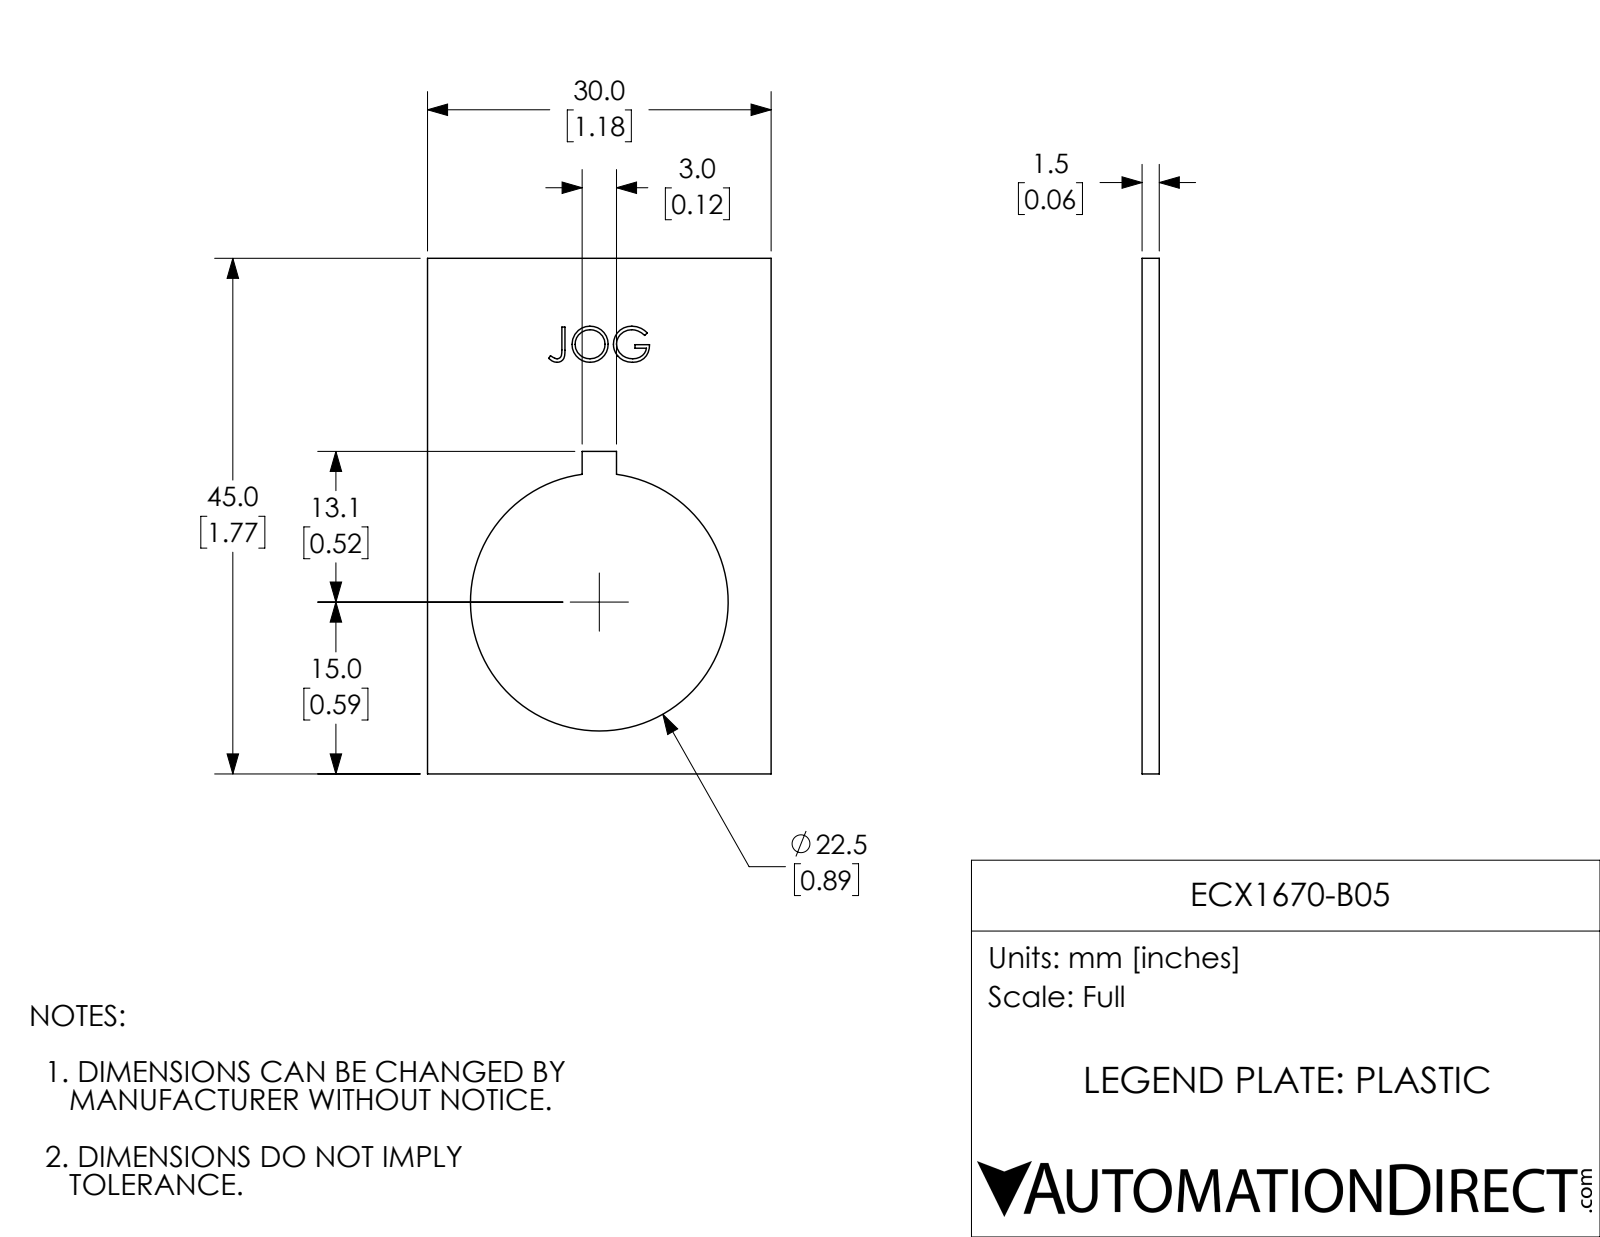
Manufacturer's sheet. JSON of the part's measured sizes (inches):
{"part_name": "ECX1670-B05", "step_written_by": "SolidWorks 2017 (AUTOMOTIVE_DESIGN)", "units": "inches", "bodies": {"solids": 1, "faces": 46, "planar": 21, "cylindrical": 3, "other": 22}, "overall_size": [1.772, 1.181, 0.059], "volume_in3": 0.087, "surface_area_in2": 3.459, "round_holes": [[0.886, 1]], "face_to_face_distances": [0.059, 1.181, 1.772, 0.058, 0.531, 0.65, 1.108, 0.663, 0.118, 0.472]}
